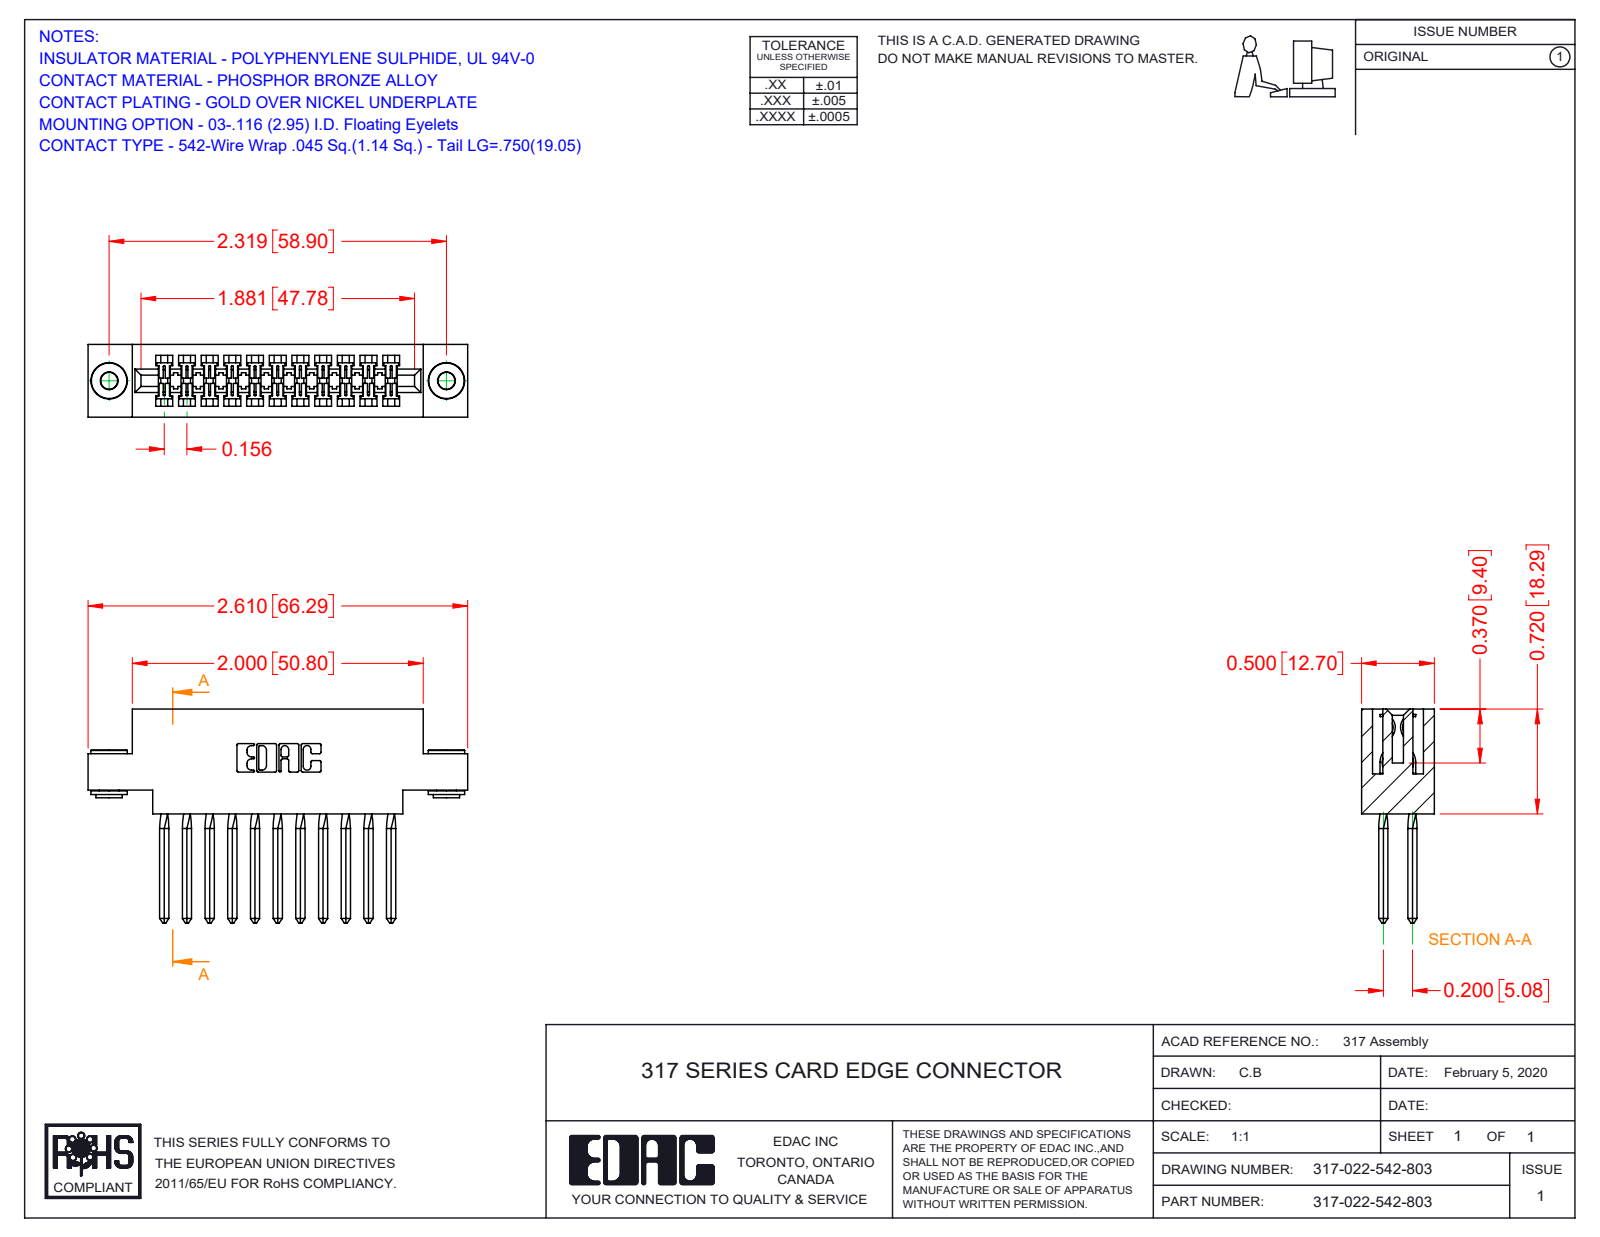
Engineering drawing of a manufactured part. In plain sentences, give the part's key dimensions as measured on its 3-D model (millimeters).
The part is named "345-250-002_345-250-002-102; 317 Part_.156 Dia - TH; 317-290-003_542; 317-022-542-803". Its 3-D file was written by "SolidWorks 2016 (CONFIG_CONTROL_DESIGN)". It is 25 solids with 1394 faces: 1080 planar, 218 cylindrical and 96 other. Overall it measures 66.3 by 37.3 by 12.7 millimeters. Its volume is 9 900 cubic millimeters and its surface area 12 980 square millimeters. Round holes: 2 of diameter 2.9, 2 of diameter 4. Round bosses or shafts: 2 of diameter 6.4, 2 of diameter 4.6, 2 of diameter 3.5. Partial cylindrical surfaces (rounded edges, fillets, slot ends): 44 of radius 0.2, 22 of radius 0.3, 6 of radius 0.2, 6 of radius 0.8, 3 of radius 0.7, 2 of radius 1.9, 2 of radius 2.3, 2 of radius 2.5. The main face-to-face distances are 12.7, 1.9, 10.8, 2.8, 2.9, 5.6, 8.9, 5.1, 3.5, 4. The hole center spacings are 58.9.
